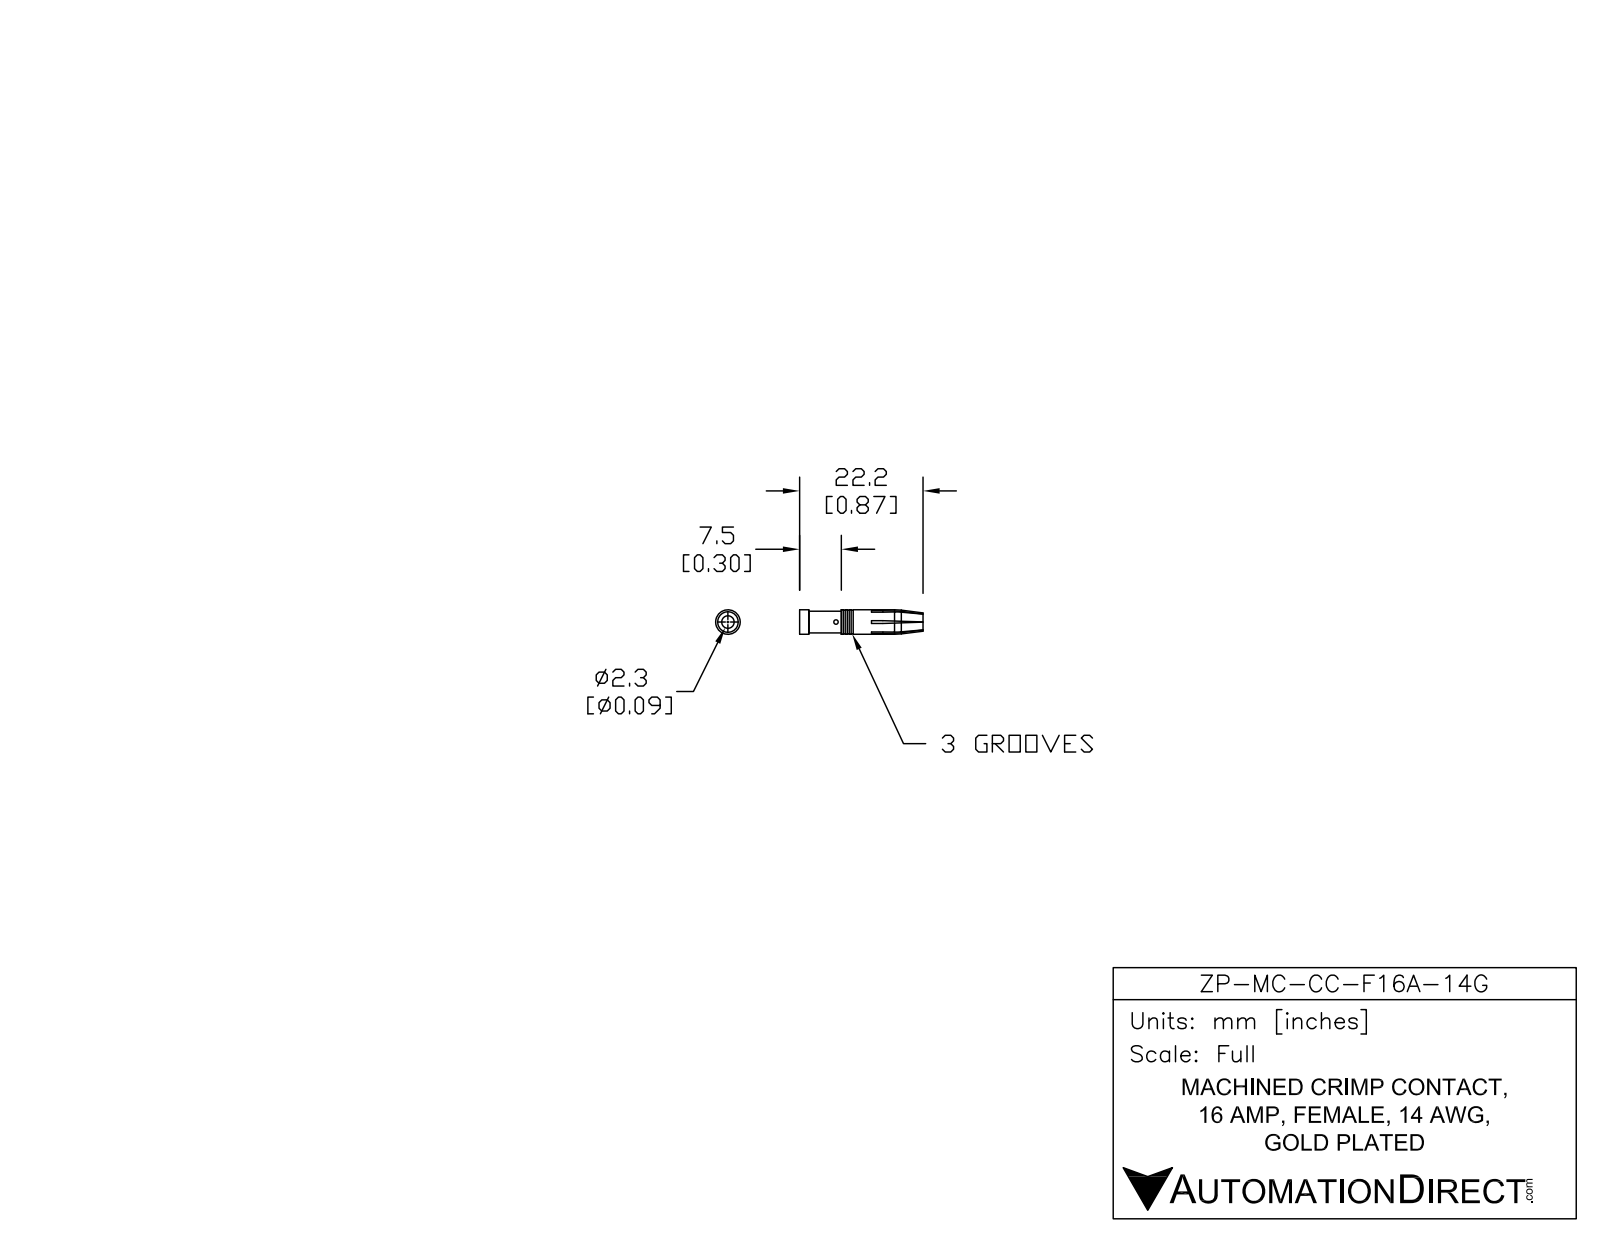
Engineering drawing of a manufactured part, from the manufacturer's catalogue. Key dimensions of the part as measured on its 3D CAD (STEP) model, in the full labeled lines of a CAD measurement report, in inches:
Part name (STEP PRODUCT): ZP-MC-CC-F16A-14G
STEP written by: SolidWorks 2014 (AUTOMOTIVE_DESIGN)
Units: inches
Bodies: 1 solid, 93 faces (45 planar, 22 cylindrical, 26 other)
Overall size (bounding box): 0.874 × 0.174 × 0.174
Volume: 0.012 in³ · Surface area: 0.815 in²
Round holes (diameter × count): ⌀0.031 ×1, ⌀0.089 ×1
Round bosses / shafts (diameter × count): ⌀0.174 ×1, ⌀0.166 ×1, ⌀0.137 ×1
Main face-to-face distances: 0.02, 0.579, 0.014, 0.028, 0.874, 0.295, 0.042, 0.559, 0.315, 0.07
